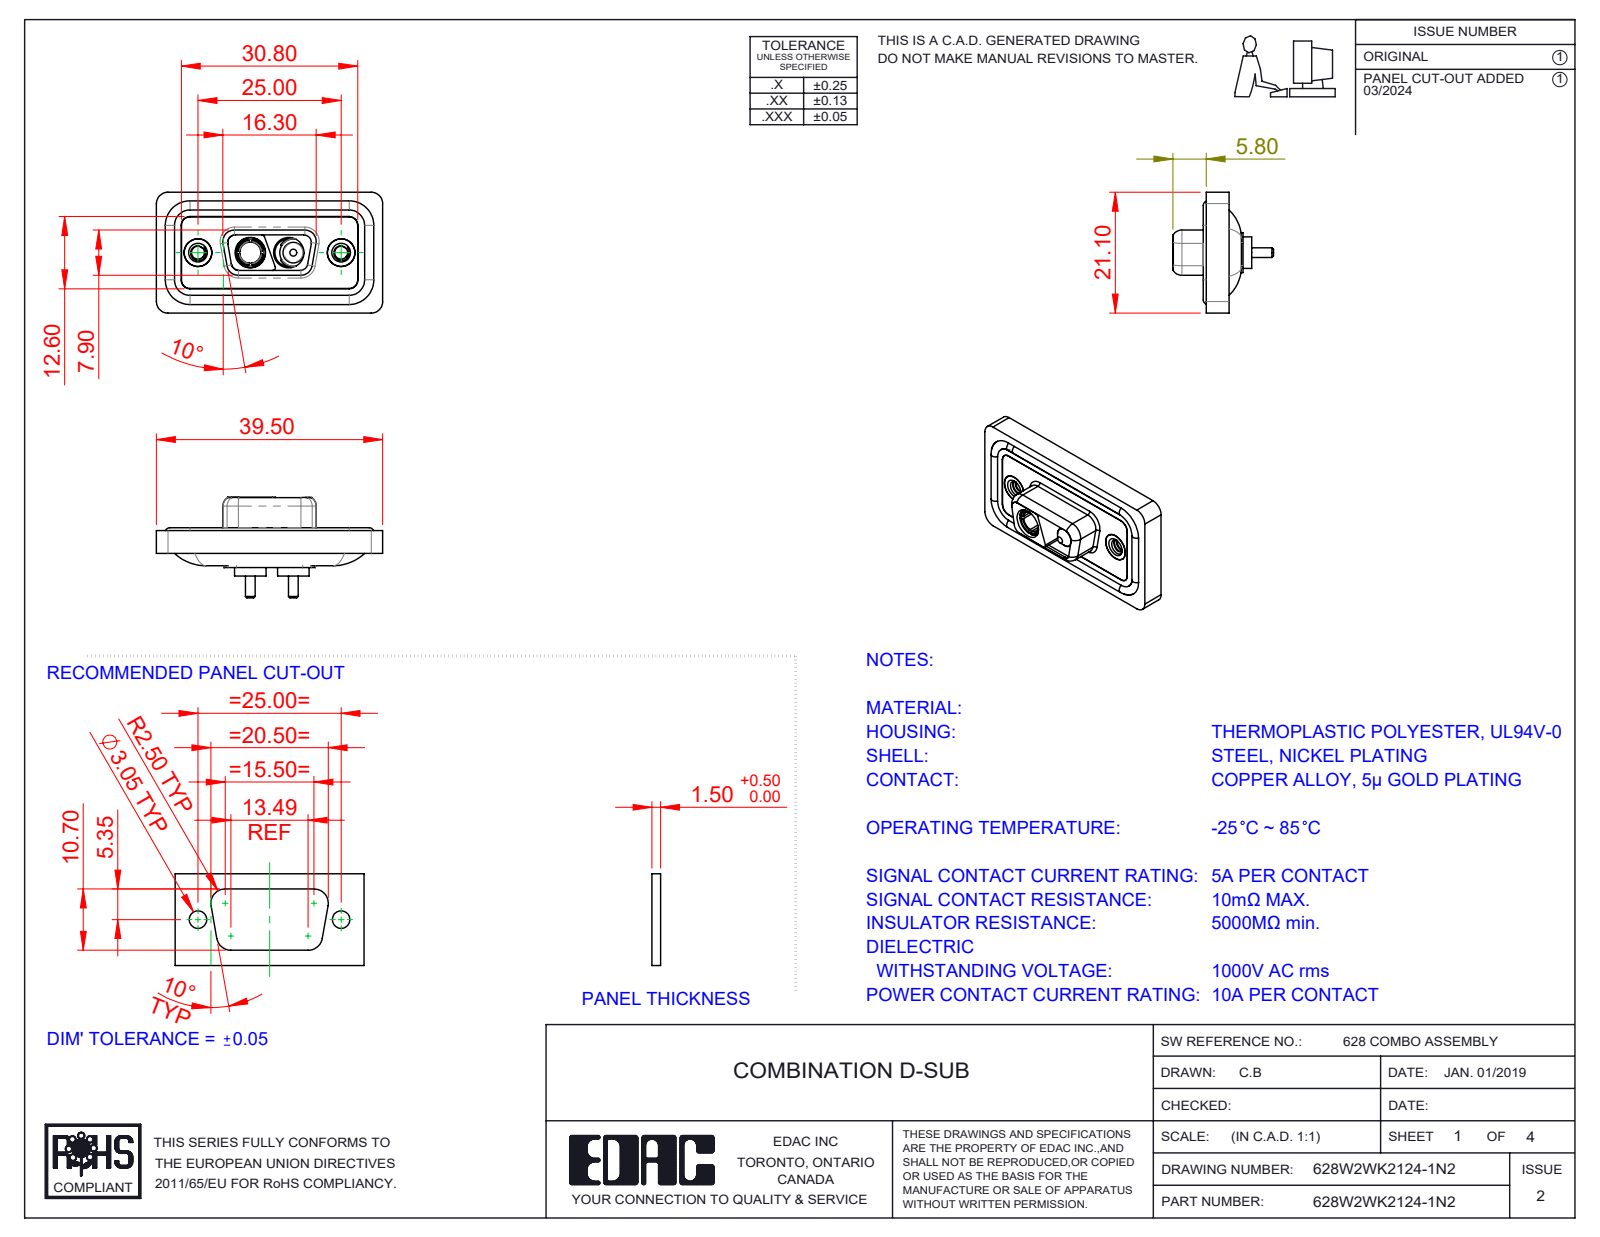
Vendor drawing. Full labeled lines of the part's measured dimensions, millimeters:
Part name (STEP PRODUCT): 628Combo Waterproof Housing_09 Contacts; Power Pin_10A S; 628W2WK2124-1N2; 628Combo Shell Front_09 Contacts (+4 more)
STEP written by: SolidWorks 2023 (CONFIG_CONTROL_DESIGN)
Units: millimetres
Bodies: 11 solids, 500 faces (144 planar, 231 cylindrical, 125 other)
Overall size (bounding box): 39.5 × 21.1 × 17.55
Volume: 4 574 mm³ · Surface area: 7 318 mm²
Round holes (diameter × count): ⌀4.85 ×4, ⌀2.26 ×2, ⌀4 ×2, ⌀4.05 ×2, ⌀5 ×2, ⌀5.3 ×2, ⌀3.7 ×1
Round bosses / shafts (diameter × count): ⌀1.6 ×4, ⌀5.5 ×2, ⌀5.2 ×2, ⌀4.95 ×2, ⌀4.8 ×2, ⌀4.75 ×2, ⌀3.75 ×2, ⌀1.7 ×2
Partial cylindrical surfaces — rounded edges, fillets, slot ends (radius × count): R1.5 ×22, R2 ×18, R1.35 ×8, R1.6 ×8, R0.5 ×6, R0.25 ×4, R0.6 ×4, R0.65 ×4
Main face-to-face distances: 0.4, 1.1, 2.9, 1.6, 0.5, 1.8, 5.65, 1.5, 5.35, 3.1
Hole centre spacings: 9.14, 15.86, 6.72, 25
